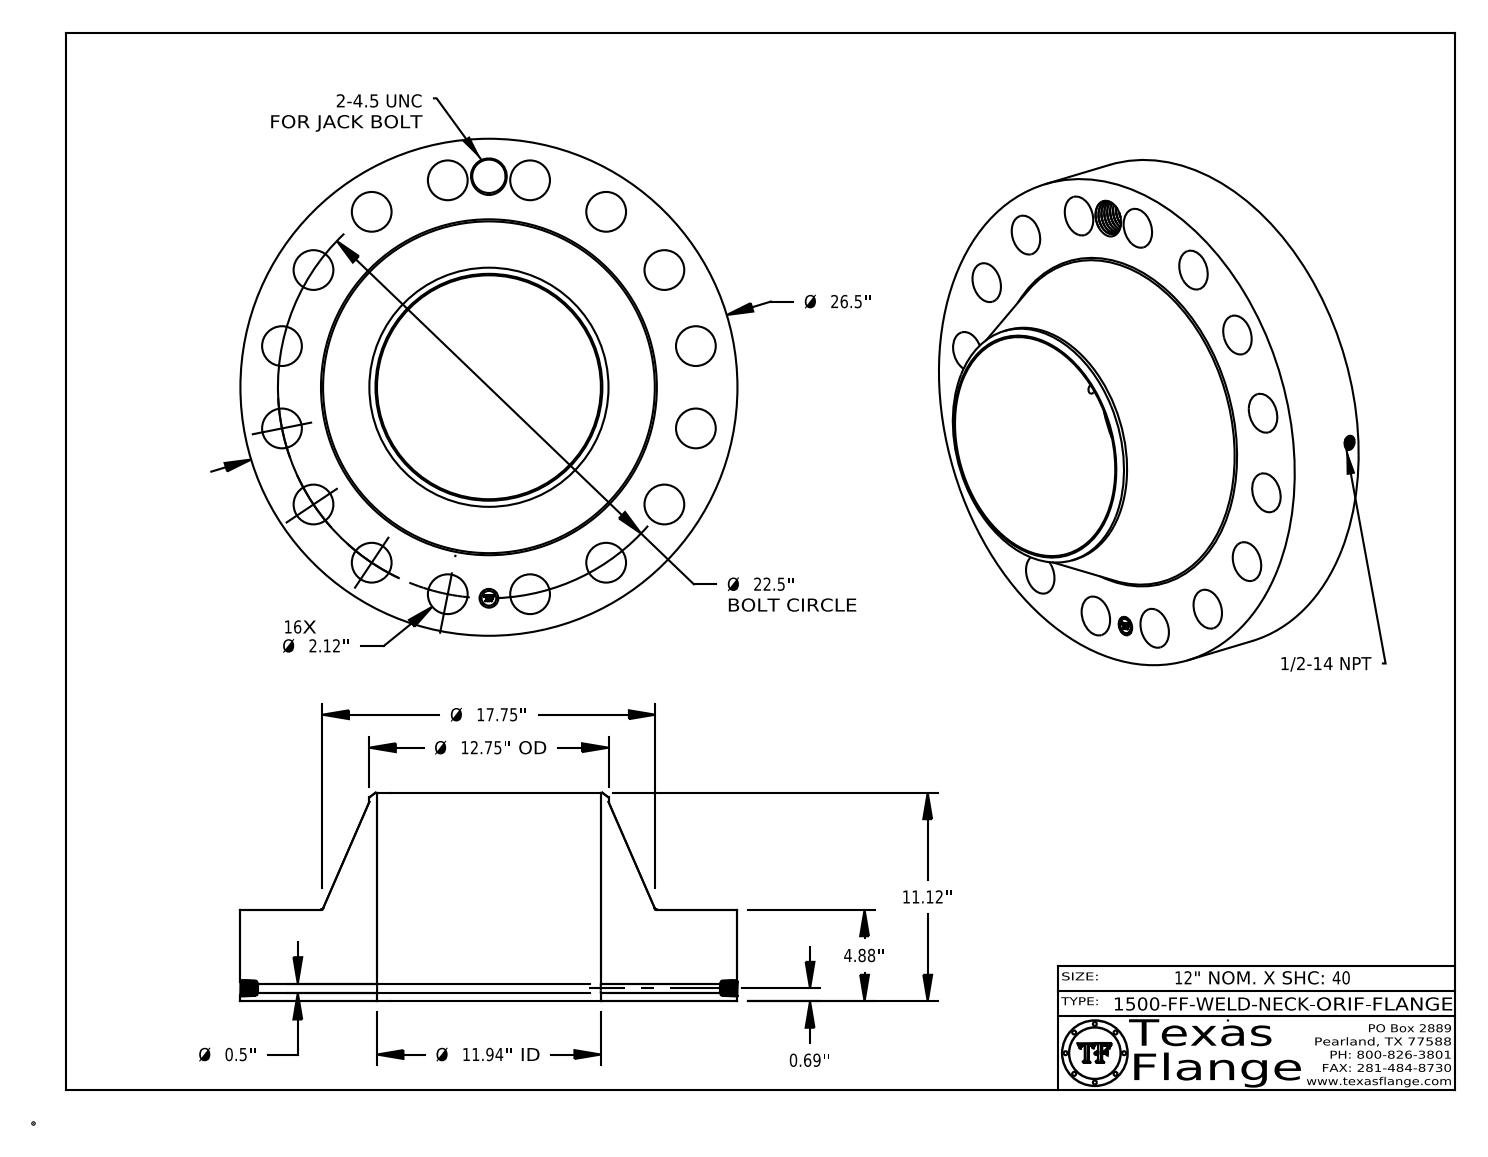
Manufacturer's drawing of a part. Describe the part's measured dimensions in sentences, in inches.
The part is named "1500-FF-WELD-NECK". Its 3-D file was written by "CATIA V5 STEP AP214 (AUTOMOTIVE_DESIGN)". It is 1 solid with 824 faces: 368 planar, 122 cylindrical and 334 other. Overall it measures 26.5 by 26.5 by 11.12 inches. Its volume is 2 275 cubic inches and its surface area 2 364 square inches. Round holes: 16 of diameter 2.12, 1 of diameter 0.5, 1 of diameter 0.672, 1 of diameter 1, 1 of diameter 1.781, 1 of diameter 11.938. Round bosses or shafts: 8 of diameter 0.061, 1 of diameter 26.5, 1 of diameter 12.75, 1 of diameter 0.788. The main face-to-face distances are 4.88, 11.12, 6.24, 4.865, 0.015, 6.255, 0.298, 0.293, 0.054, 0.248. The hole center spacings are 11.25, 8.61, 15.91, 20.787, 12.5, 18.708, 22.068, 4.389.
